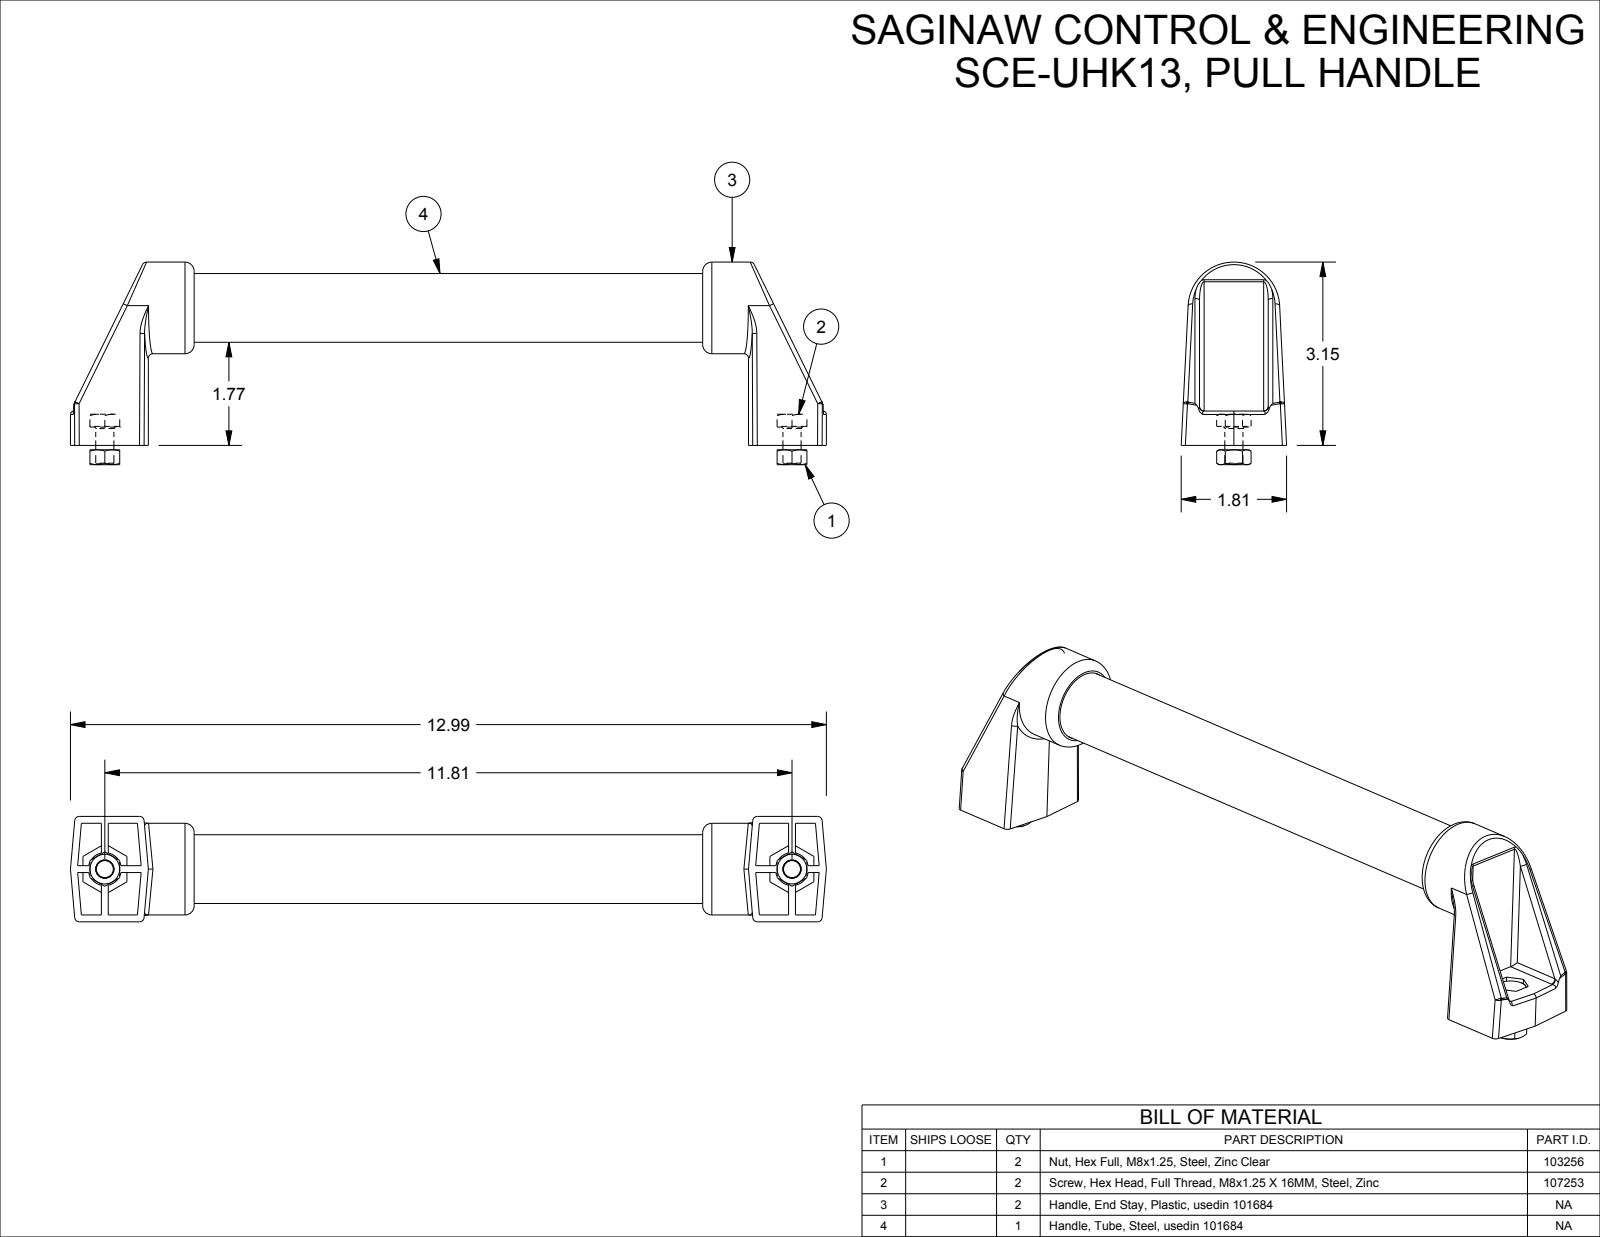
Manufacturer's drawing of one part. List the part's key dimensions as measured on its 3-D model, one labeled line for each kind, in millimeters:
Part name (STEP PRODUCT): SCE-UHK13
STEP written by: SolidWorks 2019 (AUTOMOTIVE_DESIGN)
Units: millimetres
Bodies: 7 solids, 166 faces (78 planar, 30 cylindrical, 58 other)
Overall size (bounding box): 330 × 88.4 × 46
Volume: 128 800 mm³ · Surface area: 87 230 mm²
Round holes (diameter × count): ⌀8 ×2, ⌀8.4 ×2, ⌀28.5 ×1, ⌀30.2 ×1
Round bosses / shafts (diameter × count): ⌀13 ×2, ⌀7.9 ×2, ⌀40 ×1, ⌀30 ×1
Partial cylindrical surfaces — rounded edges, fillets, slot ends (radius × count): R1.5 ×10, R2 ×4
Main face-to-face distances: 6, 268, 274, 30, 13.5, 262, 6.5, 13, 26, 248
Hole centre spacings: 300
